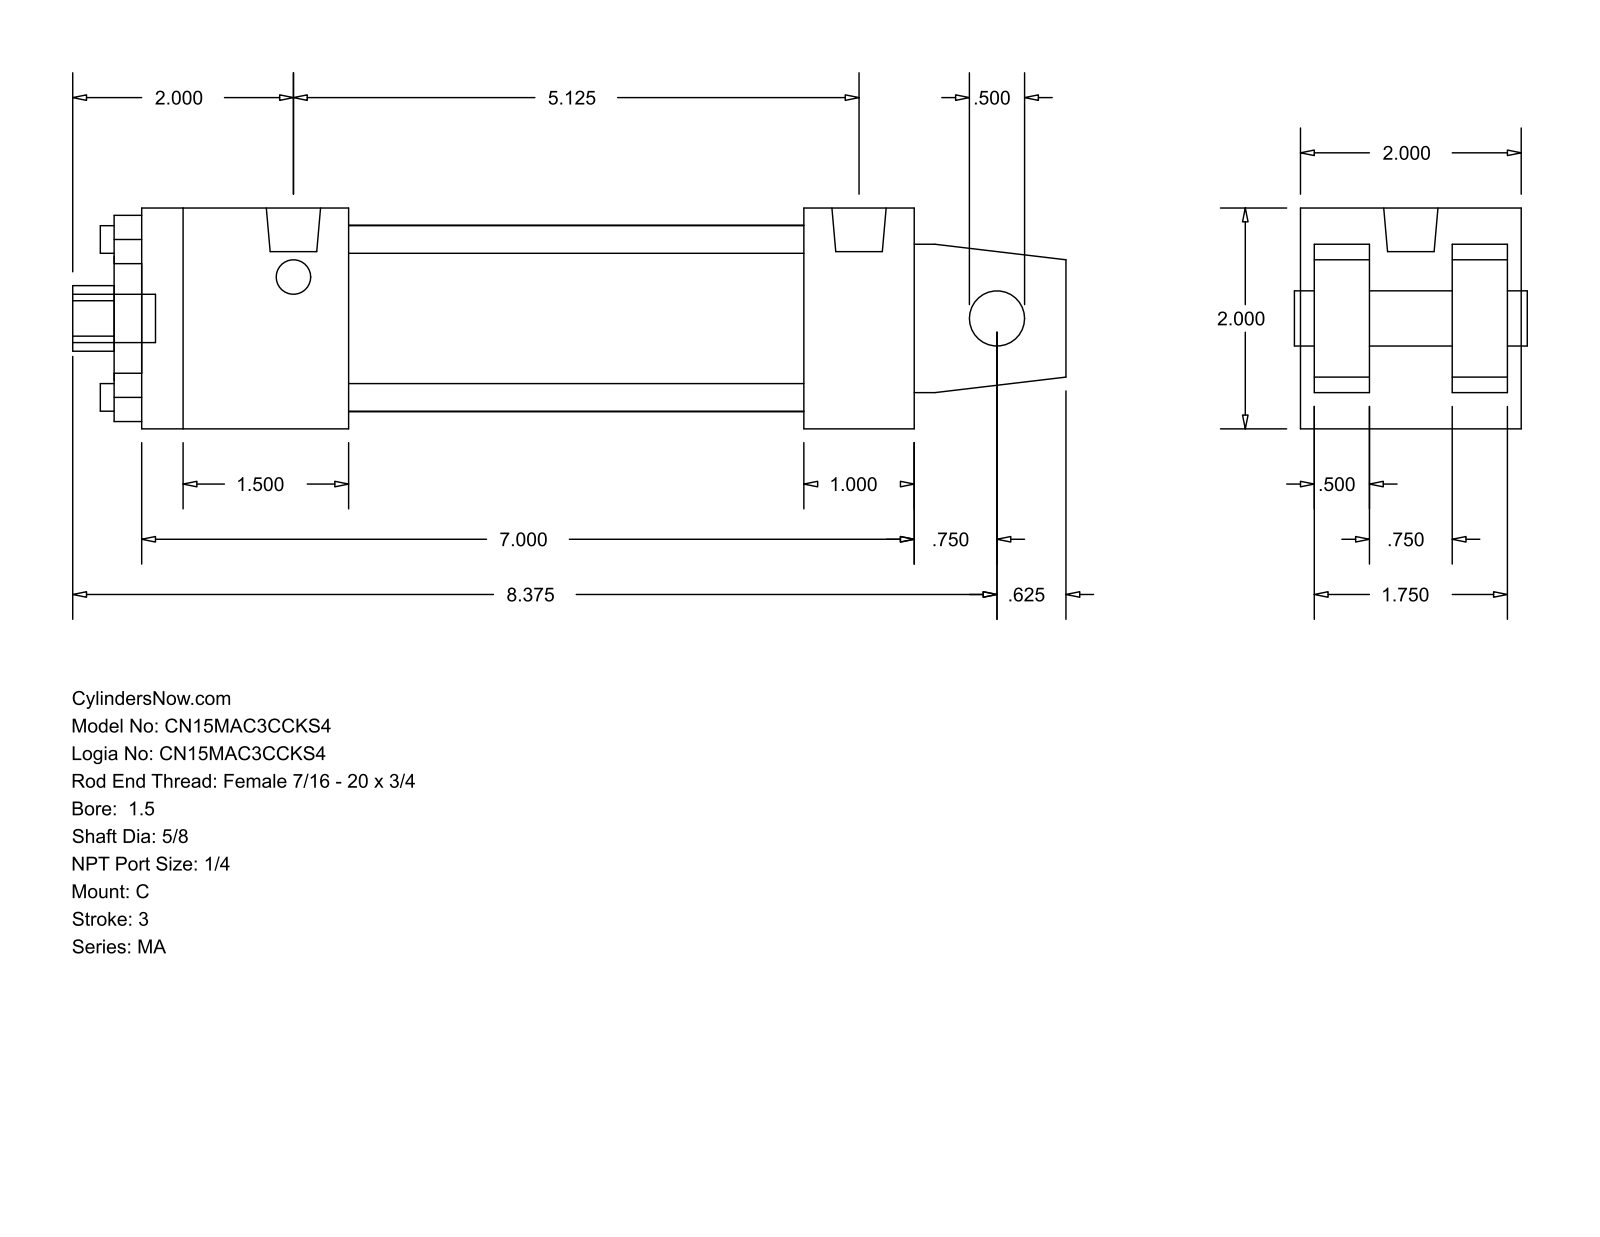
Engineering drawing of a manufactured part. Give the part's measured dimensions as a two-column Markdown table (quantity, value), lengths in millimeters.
| quantity | value |
| --- | --- |
| part name | MA_C__0150_0.625 |
| STEP written by | GSSL Pune (CONFIG_CONTROL_DESIGN) |
| units | millimeters |
| bodies | 0 solids, 103 faces (76 planar, 27 cylindrical, 0 other) |
| overall size | 228.6 × 50.8 × 50.8 |
| round holes (diameter × count) | 6.35 × 4, 12.7 × 1, 15.88 × 1, 28.57 × 1, 42.93 × 1 |
| round bosses / shafts (diameter × count) | 7.94 × 4, 12.49 × 2, 11.11 × 1 |
| partial cylindrical surfaces (radius × count) | 7.54 × 1 |
| main face-to-face distances | 50.8, 12.7, 3.17, 15.87, 34.93, 47.63, 31.76, 177.8, 152.4, 25.4 |
| hole center spacings | 25.68, 36.32, 51.36 |
